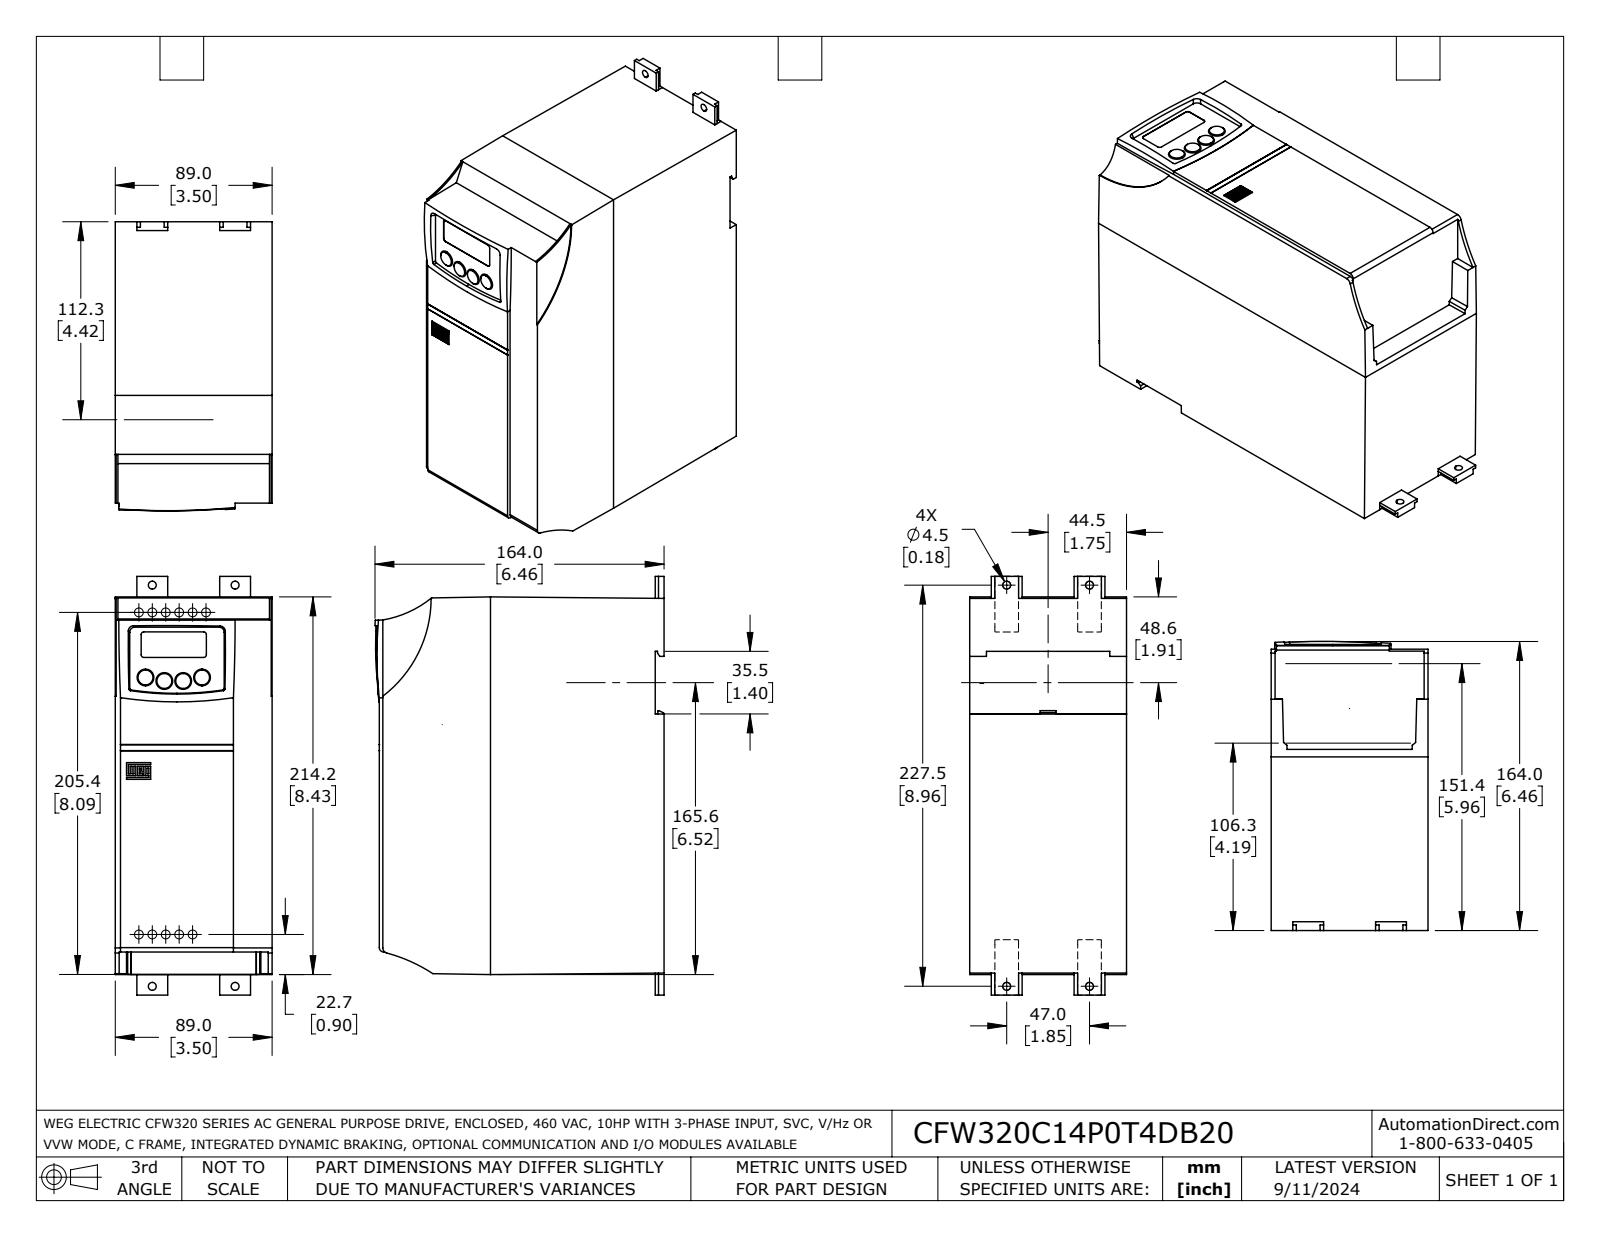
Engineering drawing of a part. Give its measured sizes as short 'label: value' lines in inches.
name: CFW320C14P0T4DB20
written by: SolidWorks 2021 (AUTOMOTIVE_DESIGN)
unit: in
bodies: 1 solid, 206 faces (165 planar, 28 cylindrical, 13 other)
size: 9.351 × 6.458 × 3.504
volume: 180.5 in³; area: 215.4 in²
holes: 4× ⌀0.177
rounds: 4× R0.059, 3× R0.118, 2× R40.039, 1× R0.039, 1× R0.098, 1× R2.362, 1× R2.75, 1× R3.543
face distances: 3.504, 6.362, 0.079, 6.283, 0.197, 6.087, 6.165, 0.039, 0.02, 3.484
hole spacings: 1.85, 8.961, 9.15
